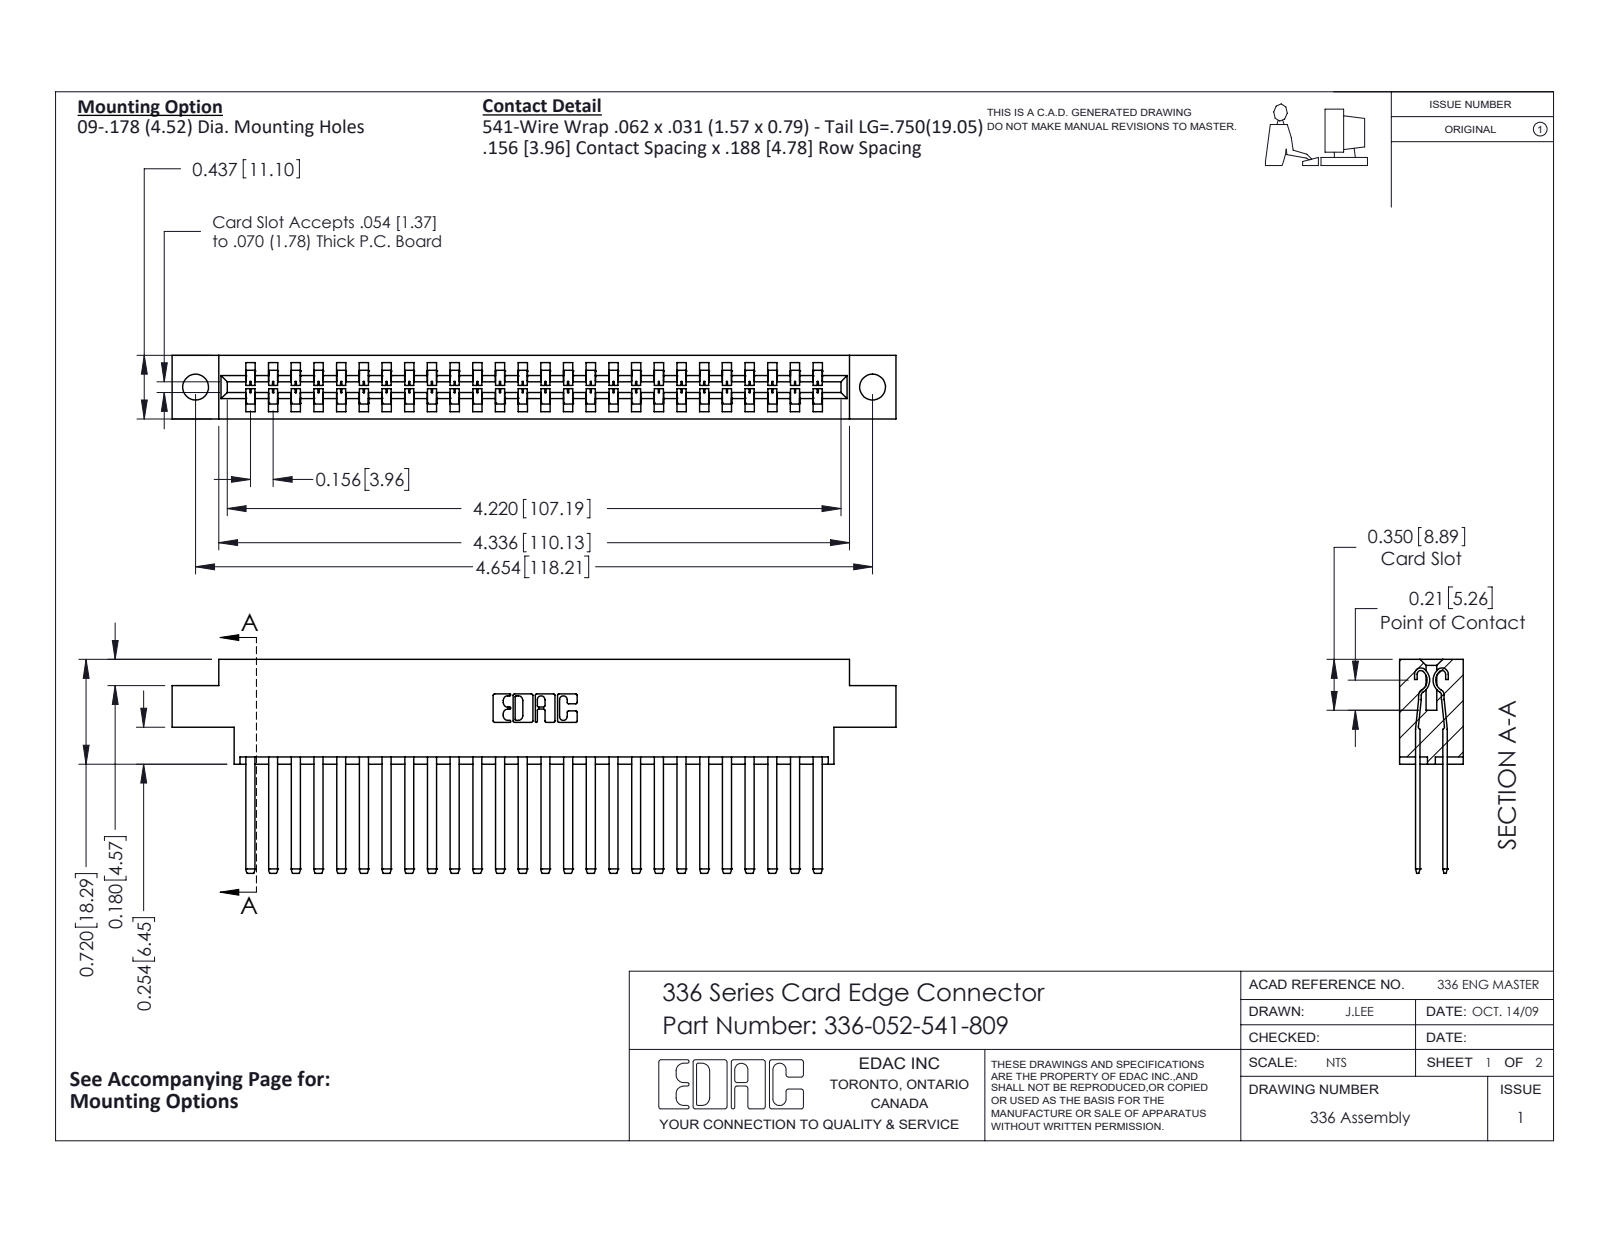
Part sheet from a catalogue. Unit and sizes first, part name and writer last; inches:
Units: inches
Overall size (bounding box): 4.977 × 1.47 × 0.437
Round holes (diameter × count): ⌀0.178 ×2
Partial cylindrical surfaces — rounded edges, fillets, slot ends (radius × count): R0.004 ×104, R0.056 ×52, R0.01 ×22, R0.007 ×6, R0.031 ×6, R0.022 ×4, R0.04 ×4, R0.026 ×3
Main face-to-face distances: 0.188, 0.328, 0.14, 0.297, 0.109, 0.031, 0.437, 0.033, 0.181, 0.256
Hole centre spacings: 4.654
Volume: 1.151 in³ · Surface area: 36.88 in²
Bodies: 53 solids, 2302 faces (1426 planar, 876 cylindrical, 0 other)
Part name (STEP PRODUCT): 336-290-001_336-290-541; 336-052-541-809; 336 Part_Offset - .178 Dia - TH
STEP written by: SolidWorks 2020 (CONFIG_CONTROL_DESIGN)
